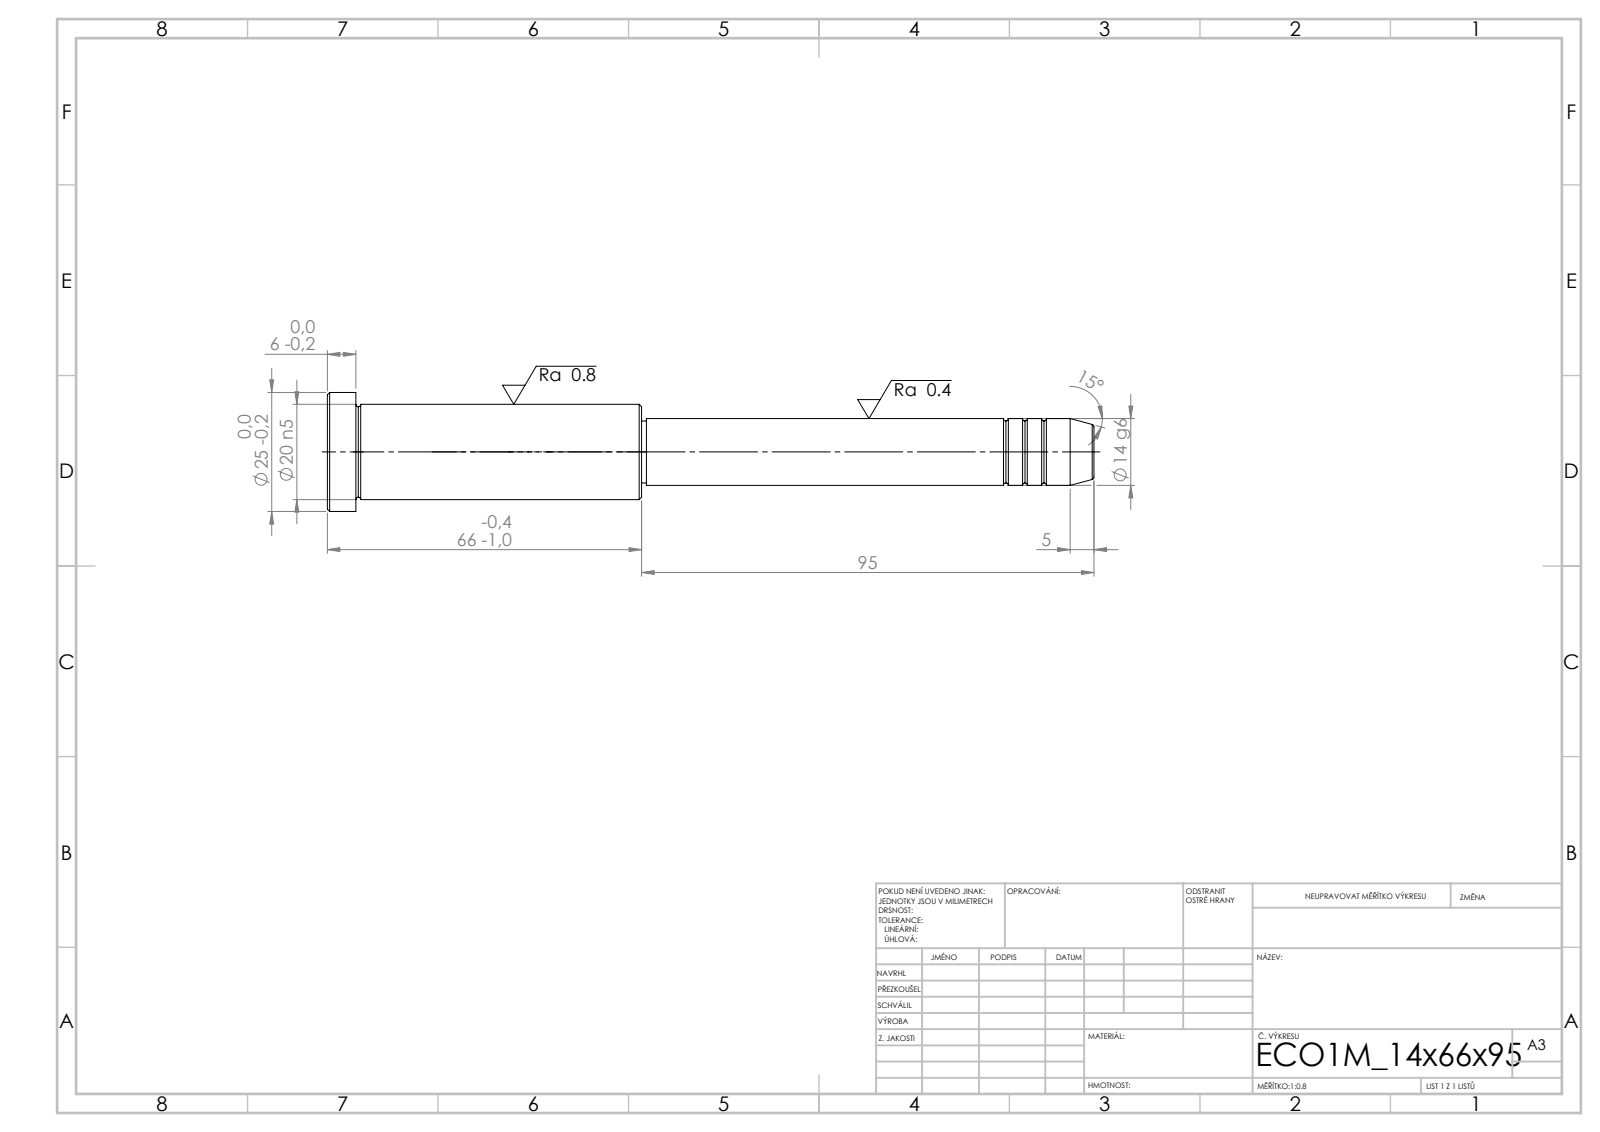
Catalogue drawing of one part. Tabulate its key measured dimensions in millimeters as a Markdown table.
| quantity | value |
| --- | --- |
| STEP written by | SolidWorks 2019 (CONFIG_CONTROL_DESIGN) |
| units | millimeters |
| bodies | 1 solid, 43 faces (5 planar, 14 cylindrical, 24 other) |
| overall size | 161 × 25 × 25 |
| volume | 36 167 mm³ |
| surface area | 9 426 mm² |
| round bosses / shafts (diameter × count) | 25 × 1, 20 × 1, 14 × 1, 13 × 1 |
| main face-to-face distances | 6, 60, 66, 95, 155, 161, 94, 1, 61, 67 |
